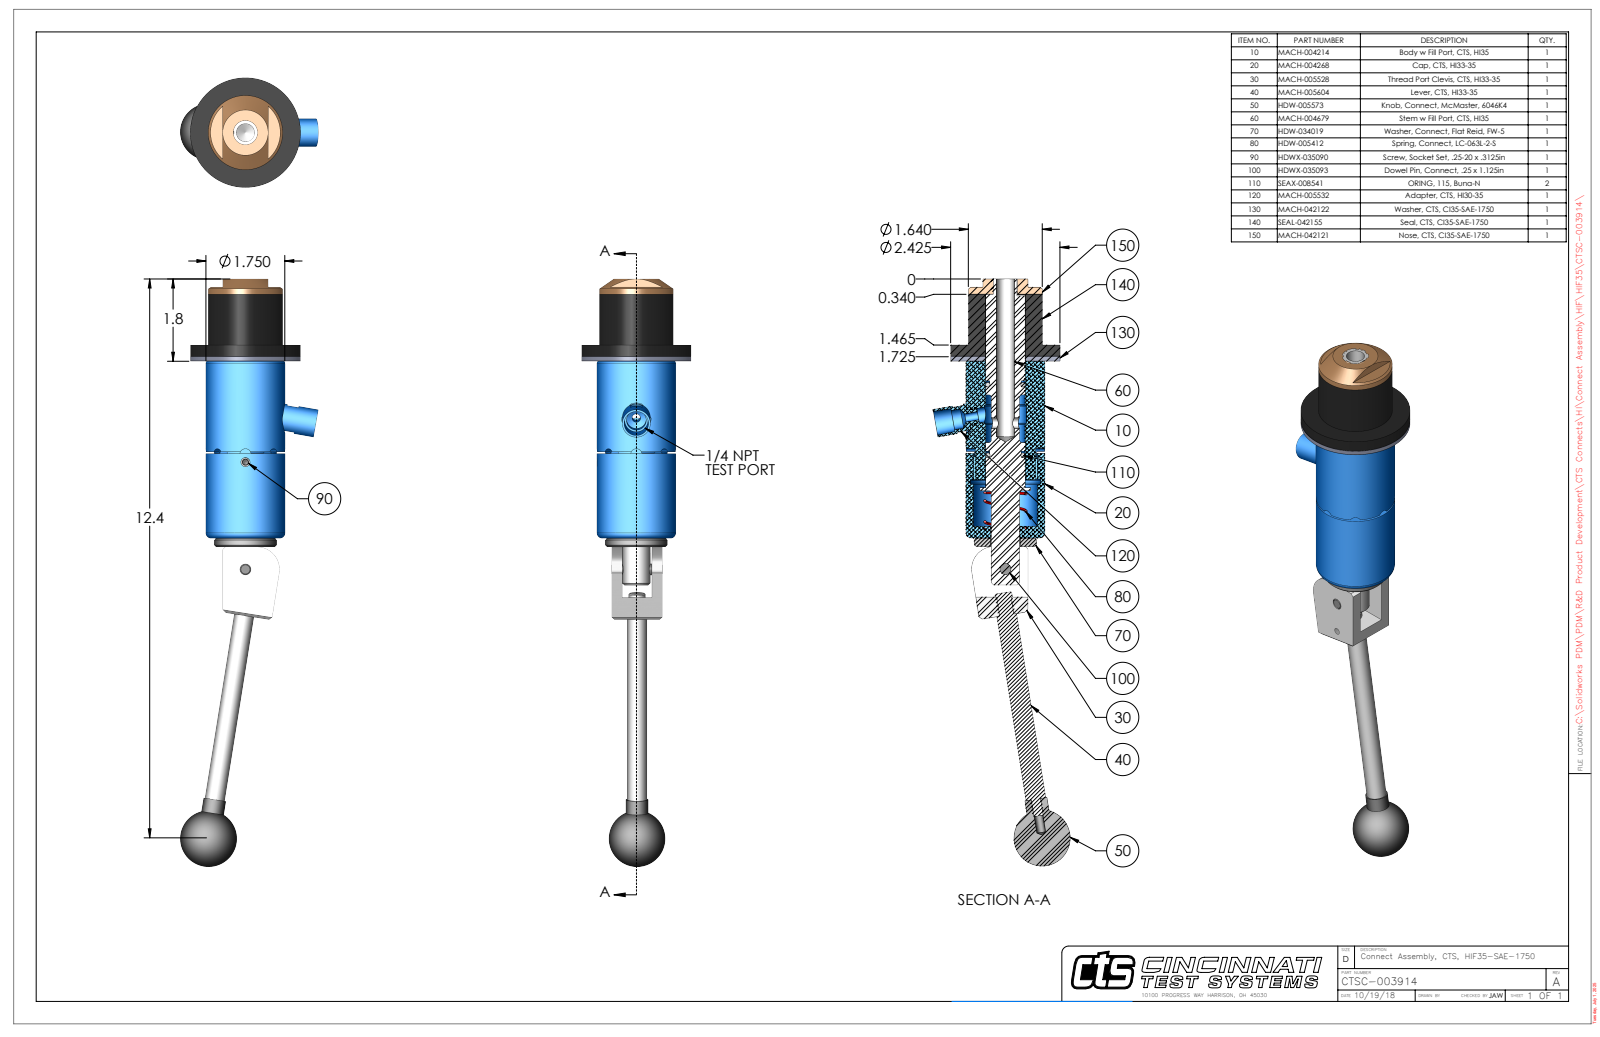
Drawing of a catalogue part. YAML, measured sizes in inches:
part_name: "CTSC-003914"
step_written_by: "SolidWorks 2023 (AUTOMOTIVE_DESIGN)"
units: inches
bodies: {solids: 9, faces: 285, planar: 104, cylindrical: 119, other: 62}
overall_size: [13.02, 3.043, 2.425]
volume: 16.9
surface_area: 105
round_holes:
  - {diameter: 0.201, count: 2}
  - {diameter: 0.15, count: 1}
  - {diameter: 0.187, count: 1}
  - {diameter: 0.249, count: 1}
  - {diameter: 0.25, count: 1}
  - {diameter: 0.251, count: 1}
  - {diameter: 0.313, count: 1}
  - {diameter: 0.406, count: 1}
  - {diameter: 0.438, count: 1}
  - {diameter: 0.531, count: 1}
  - {diameter: 0.635, count: 1}
  - {diameter: 0.656, count: 1}
round_bosses_or_shafts:
  - {diameter: 0.25, count: 2}
  - {diameter: 2.425, count: 1}
  - {diameter: 1.75, count: 1}
  - {diameter: 1.64, count: 1}
  - {diameter: 1.38, count: 1}
  - {diameter: 0.869, count: 1}
  - {diameter: 0.625, count: 1}
  - {diameter: 0.62, count: 1}
partial_cylinders:
  - {radius: 0.125, count: 4}
  - {radius: 0.029, count: 2}
  - {radius: 0.166, count: 1}
  - {radius: 0.246, count: 1}
  - {radius: 0.33, count: 1}
  - {radius: 0.5, count: 1}
  - {radius: 0.695, count: 1}
  - {radius: 0.815, count: 1}
face_to_face_distances: [0.11, 1.375, 1.485, 0.25, 1.125, 0.36, 5.405, 4.28, 4.03, 3.92]
hole_center_spacings: [0.74, 2.376, 3.116]
